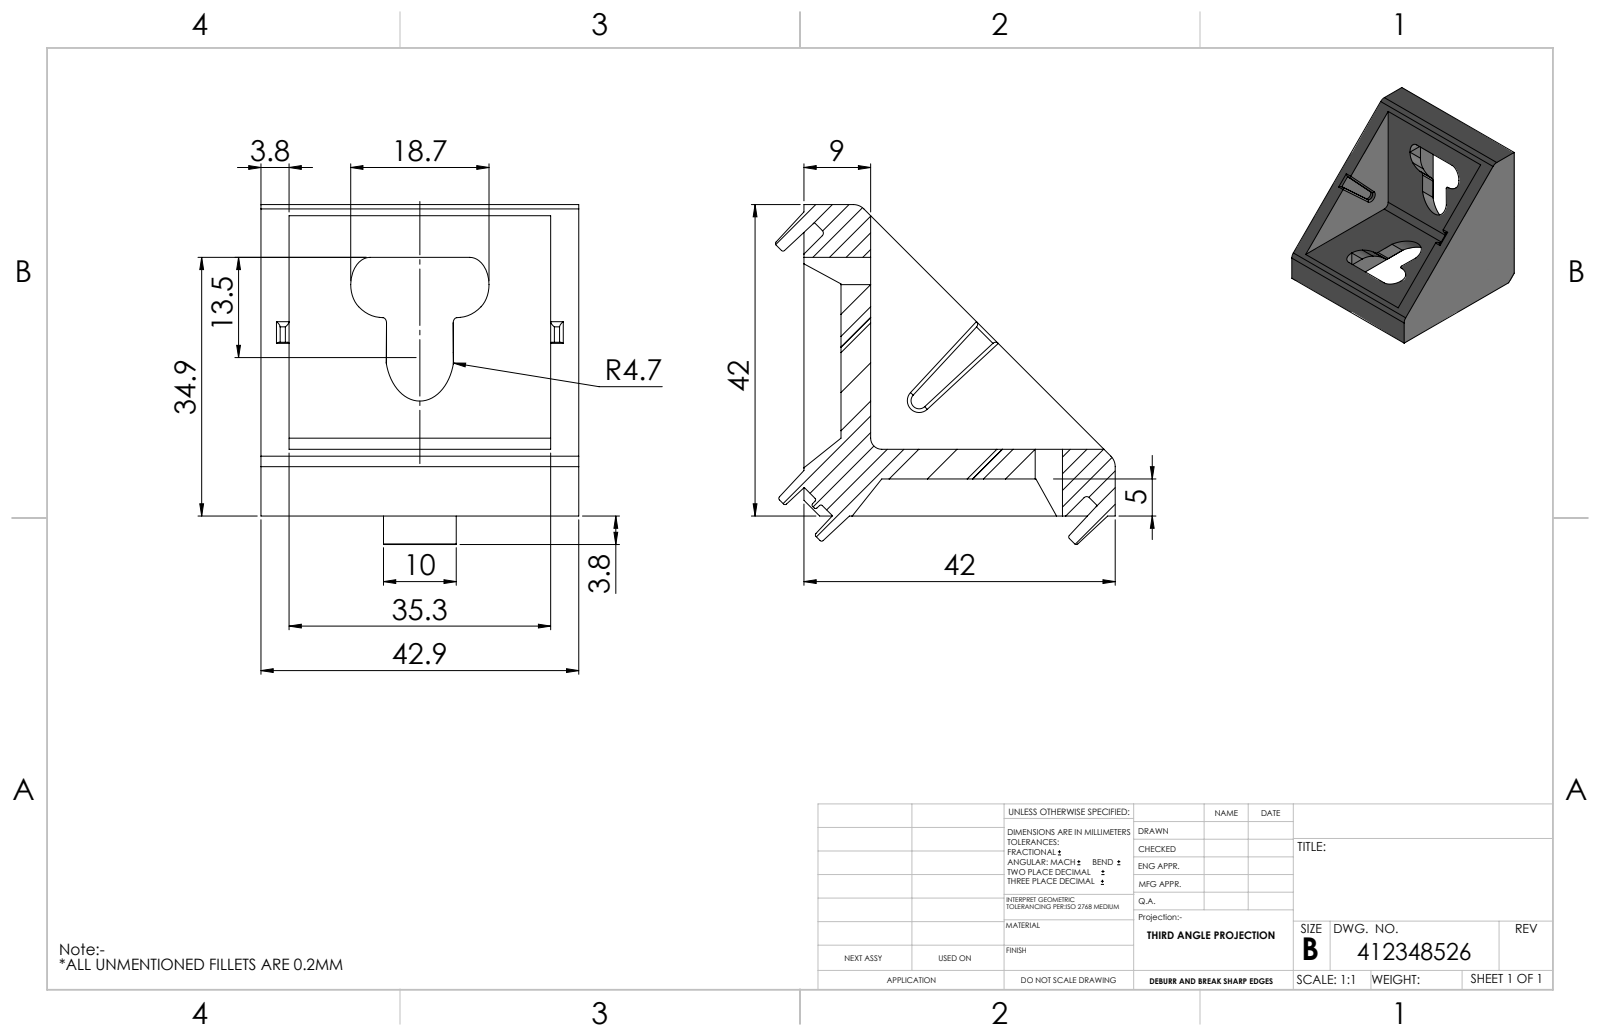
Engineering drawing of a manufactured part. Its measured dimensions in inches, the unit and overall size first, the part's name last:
Units: inches
Overall size (bounding box): 1.805 × 1.805 × 1.688
Partial cylindrical surfaces — rounded edges, fillets, slot ends (radius × count): R0.039 ×22, R0.02 ×14, R0.012 ×8, R0.01 ×4, R0.102 ×4, R0.205 ×4, R0.079 ×2, R0.183 ×2
Main face-to-face distances: 0.354, 1.688, 0.149, 1.539, 0.157, 0.197, 1.299, 1.457, 1.654, 0.133
Volume: 1.336 in³ · Surface area: 19.21 in²
Bodies: 1 solid, 192 faces (103 planar, 71 cylindrical, 18 other)
Part name (STEP PRODUCT): 412348526 Winkel 43x42
STEP written by: Autodesk Inventor 2019 (AUTOMOTIVE_DESIGN)
